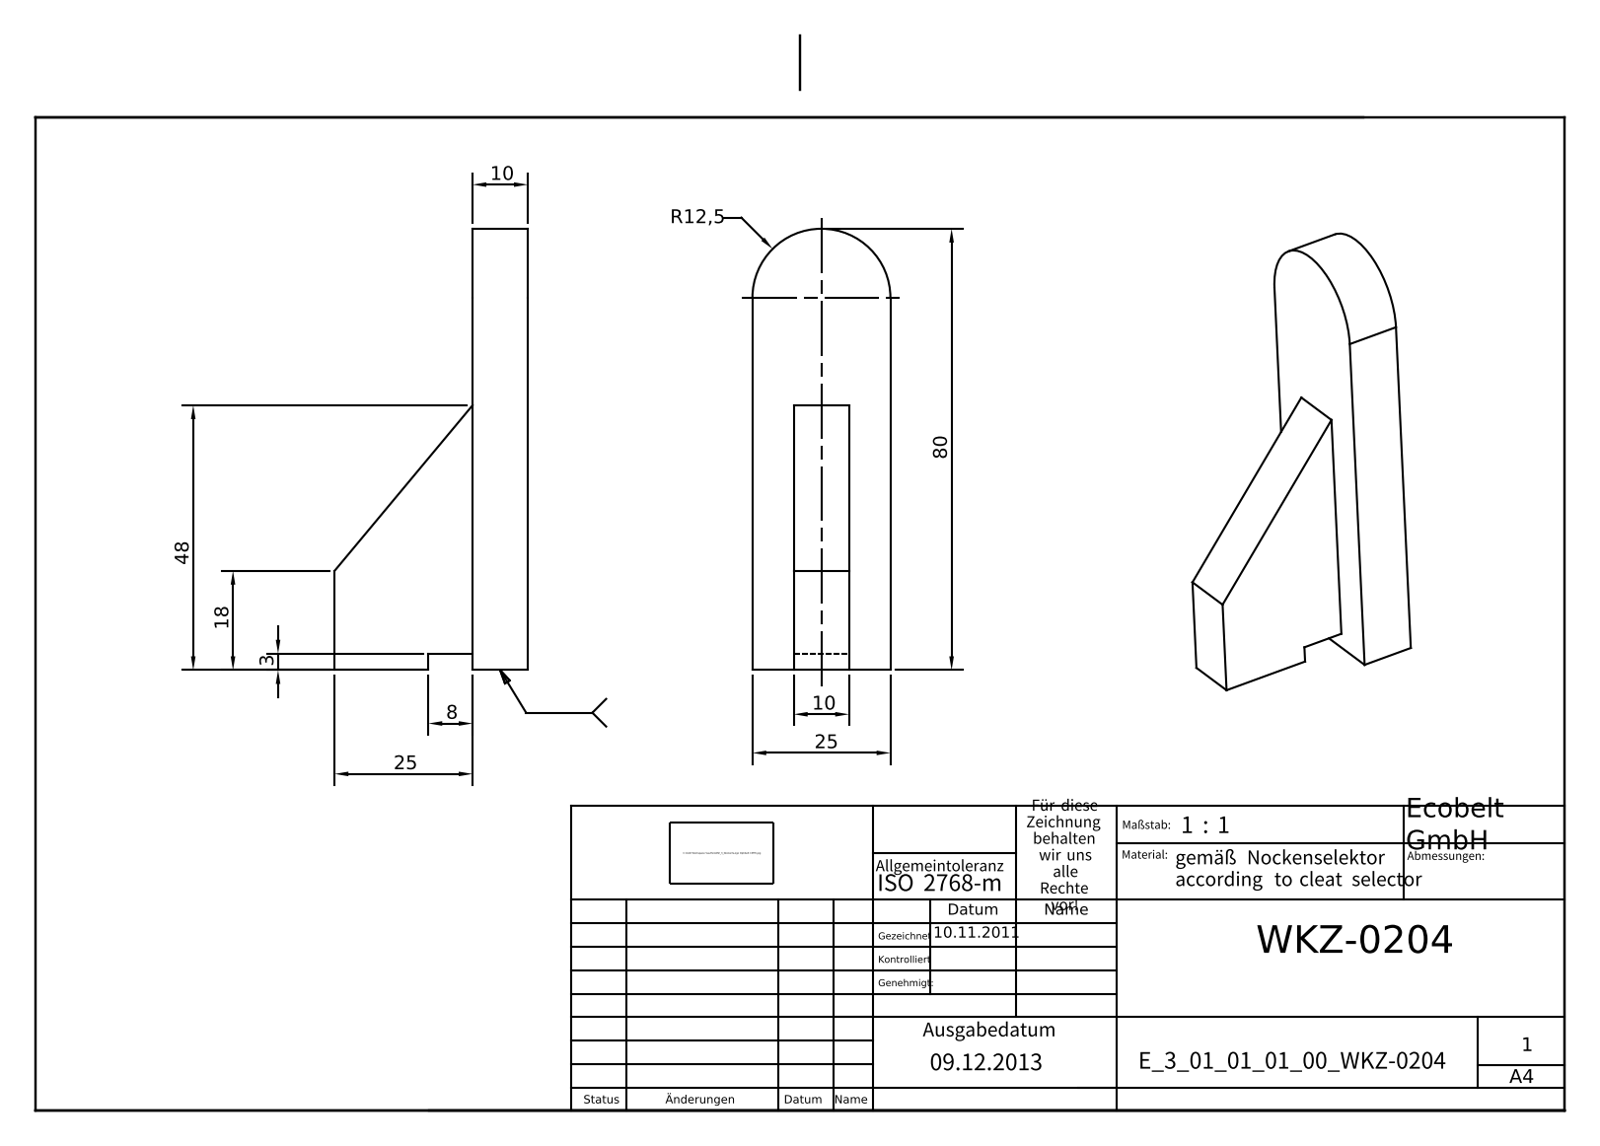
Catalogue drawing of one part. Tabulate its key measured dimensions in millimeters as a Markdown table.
| quantity | value |
| --- | --- |
| part name | E_3_01_01_01_00_WKZ-0204 |
| STEP written by | Autodesk Inventor 2021 (AUTOMOTIVE_DESIGN) |
| units | millimeters |
| bodies | 1 solid, 13 faces (12 planar, 1 cylindrical, 0 other) |
| overall size | 80 × 35 × 25 |
| volume | 27 339 mm³ |
| surface area | 7 861 mm² |
| partial cylindrical surfaces (radius × count) | 12.5 × 1 |
| main face-to-face distances | 10, 7.5, 17.5, 25, 35, 3, 18, 8, 17 |
